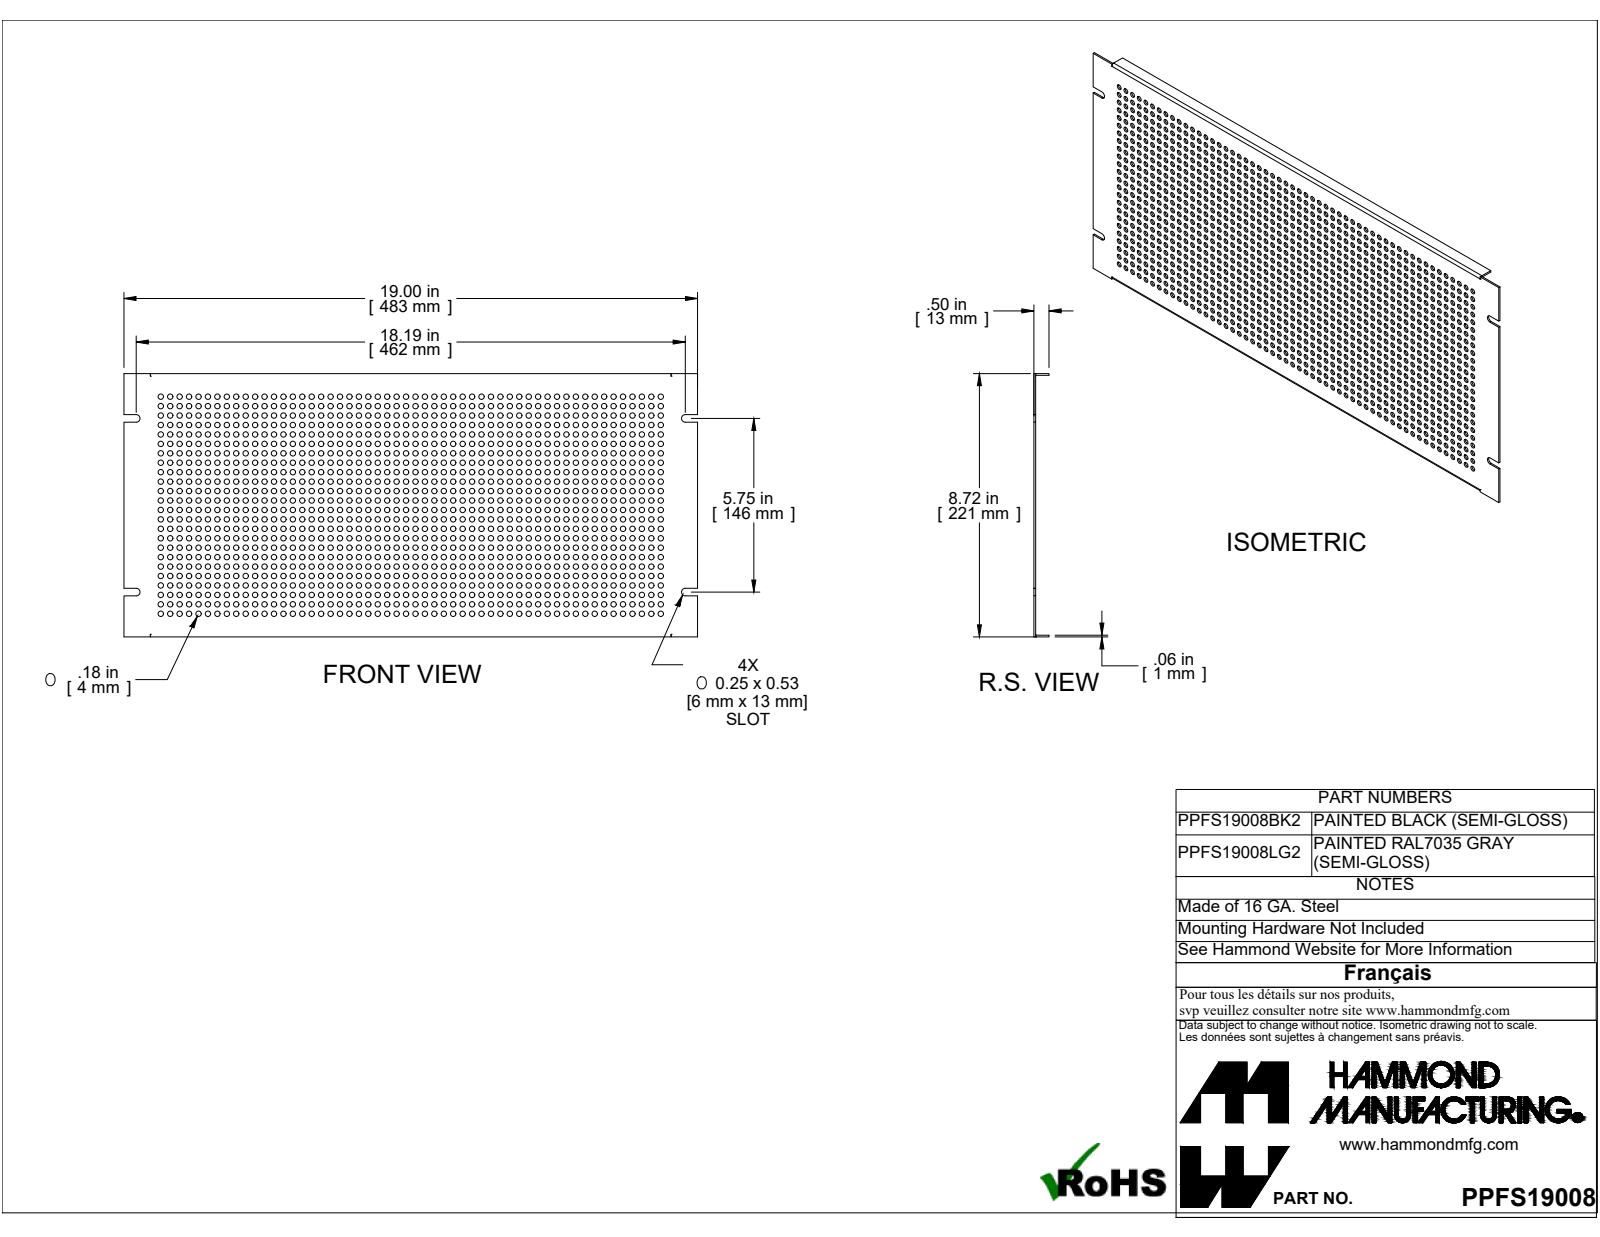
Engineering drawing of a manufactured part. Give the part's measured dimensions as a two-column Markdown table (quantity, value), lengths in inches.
| quantity | value |
| --- | --- |
| part name | PPFS19008BK2 |
| STEP written by | SolidWorks 2019 (CONFIG_CONTROL_DESIGN) |
| units | inches |
| bodies | 1 solid, 1342 faces (38 planar, 1304 cylindrical, 0 other) |
| overall size | 19 × 8.718 × 0.5 |
| volume | 8.418 in³ |
| surface area | 340 in² |
| round holes (diameter × count) | 0.177 × 1296 |
| partial cylindrical surfaces (radius × count) | 0.125 × 4, 0.029 × 2, 0.086 × 2 |
| main face-to-face distances | 0.057, 8.661, 8.718, 8.604, 0.5, 0.443, 19, 0.875, 18.125, 1.359 |
| hole center spacings | 1.25, 0.313, 0.937, 2.5, 1.563, 0.625, 0.312, 2.187 |
